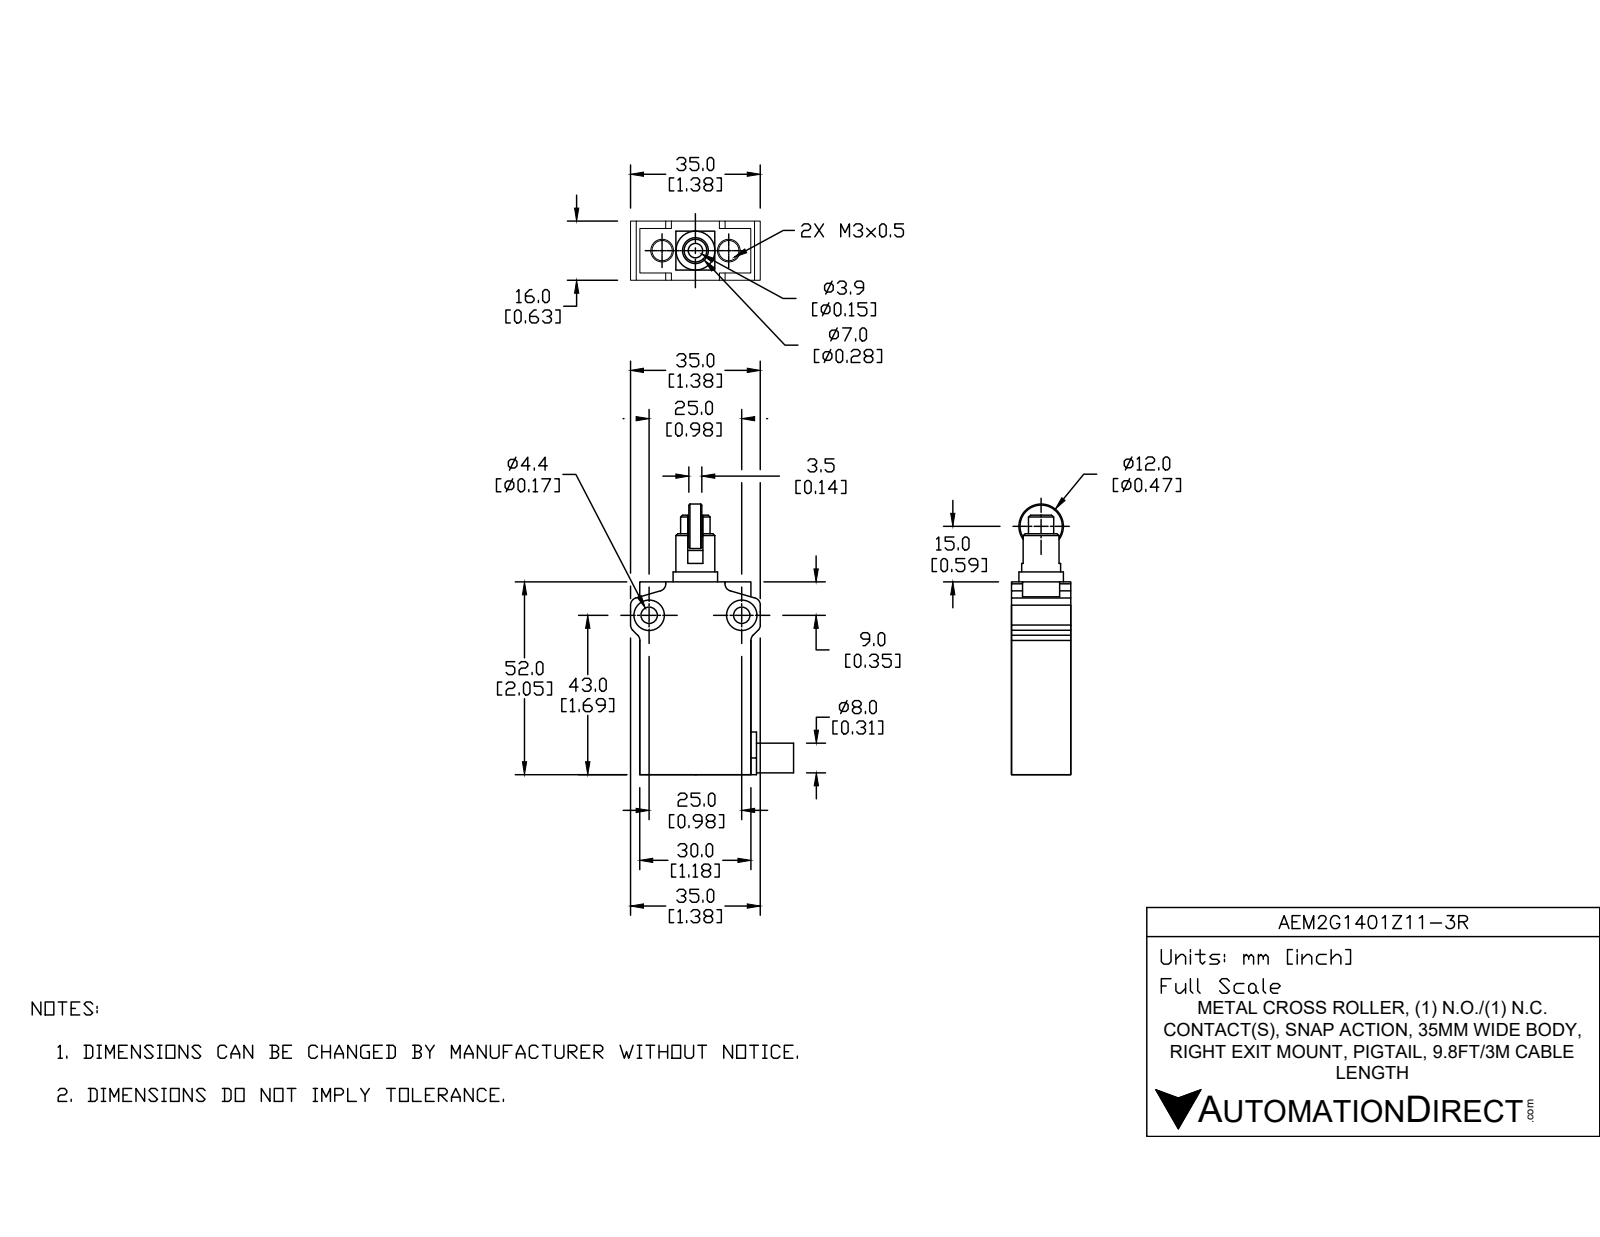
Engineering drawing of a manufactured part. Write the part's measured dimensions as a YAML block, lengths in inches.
part_name: "AEM2G1401Z11-3R"
step_written_by: "SolidWorks 2017 (AUTOMOTIVE_DESIGN)"
units: inches
bodies: {solids: 5, faces: 129, planar: 64, cylindrical: 52, other: 13}
overall_size: [2.756, 1.87, 0.63]
volume: 1.516
surface_area: 14.04
round_holes:
  - {diameter: 0.118, count: 2}
  - {diameter: 0.173, count: 2}
  - {diameter: 0.323, count: 2}
  - {diameter: 0.317, count: 1}
round_bosses_or_shafts:
  - {diameter: 0.472, count: 2}
  - {diameter: 0.413, count: 1}
  - {diameter: 0.323, count: 1}
  - {diameter: 0.313, count: 1}
  - {diameter: 0.22, count: 1}
partial_cylinders:
  - {radius: 0.079, count: 8}
  - {radius: 0.256, count: 1}
face_to_face_distances: [0.63, 1.181, 1.929, 0.472, 1.74, 0.189, 0.15, 0.157, 0.51, 0.671]
hole_center_spacings: [0.374, 0.748, 0.984]
